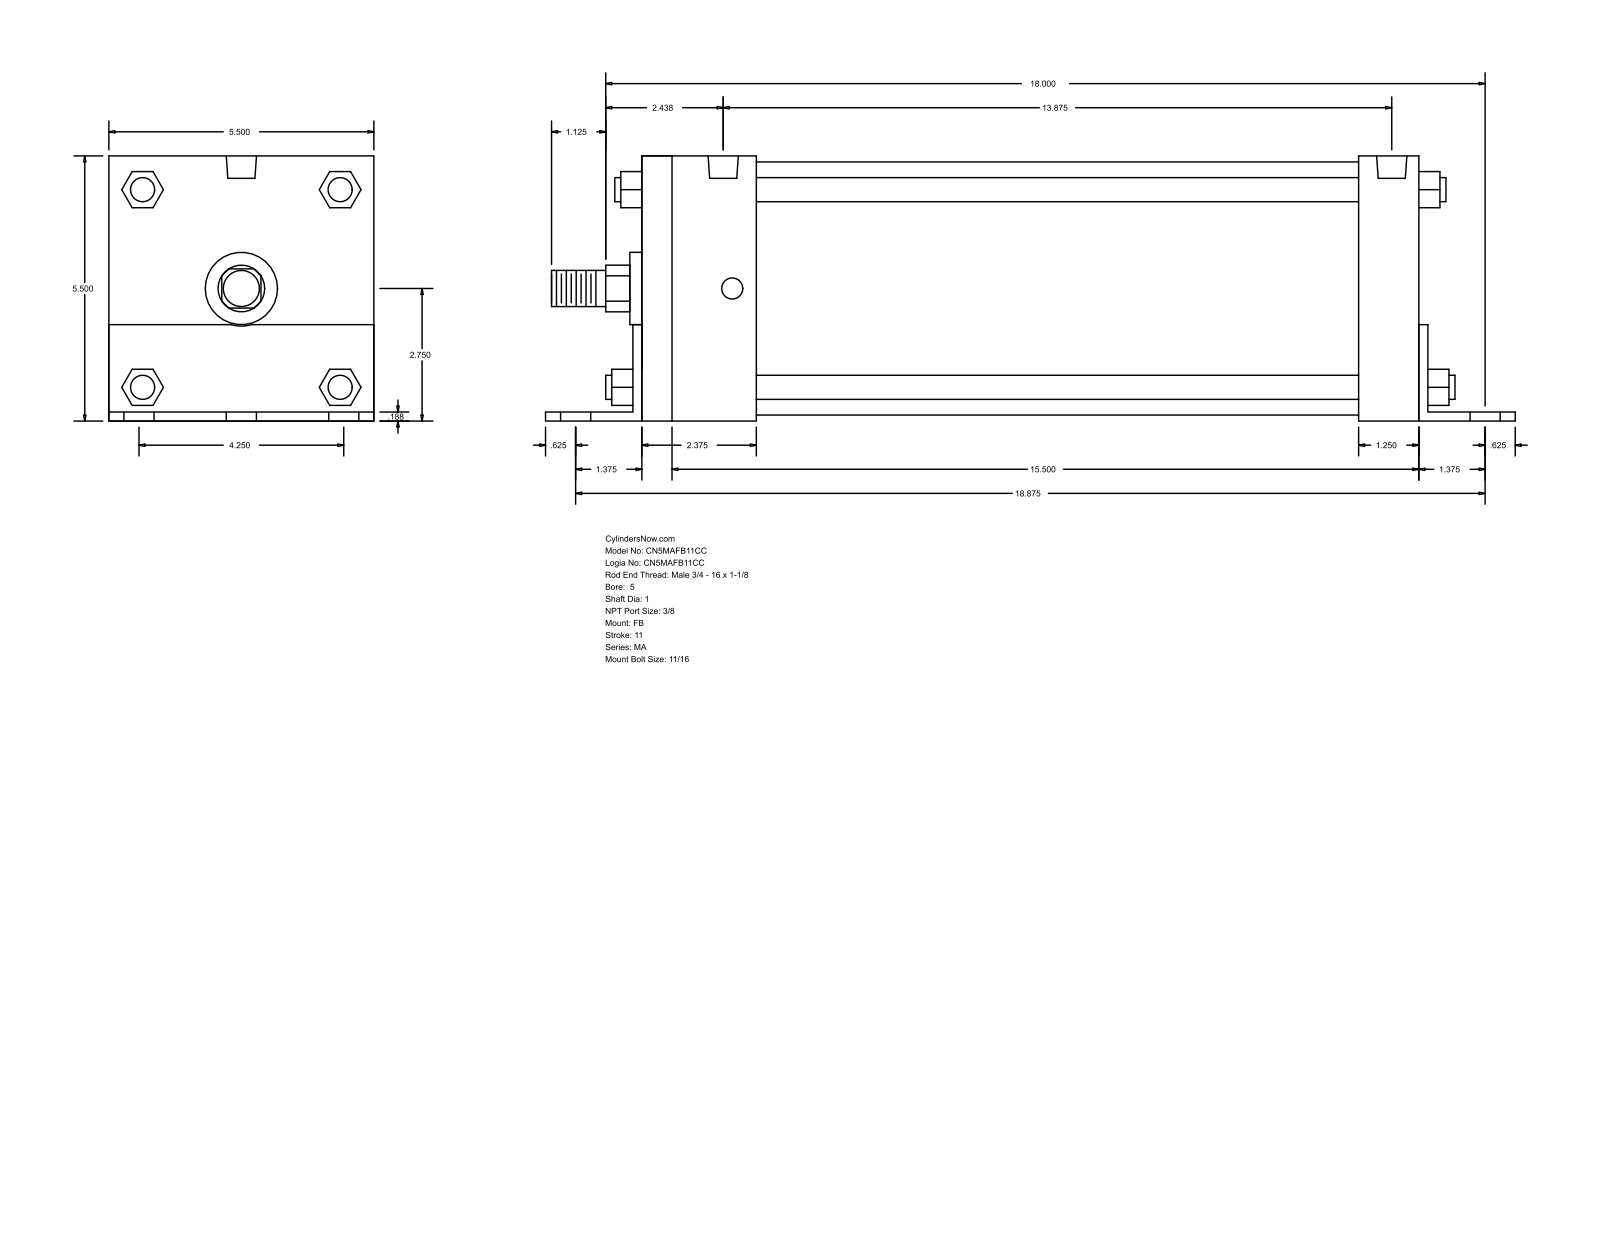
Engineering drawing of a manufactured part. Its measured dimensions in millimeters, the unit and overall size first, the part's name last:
Units: millimetres
Overall size (bounding box): 511.18 × 139.75 × 139.7
Round holes (diameter × count): ⌀17.46 ×6, ⌀11.11 ×4, ⌀15.93 ×2
Round bosses / shafts (diameter × count): ⌀12.7 ×4, ⌀133.35 ×1, ⌀38.1 ×1, ⌀25.4 ×1, ⌀19.05 ×1
Partial cylindrical surfaces — rounded edges, fillets, slot ends (radius × count): R12.29 ×1, R19.81 ×1
Main face-to-face distances: 139.7, 4.76, 139.75, 4.71, 134.99, 409.57, 4.77, 414.34, 414.33, 419.1
Hole centre spacings: 53.98, 482.46, 479.43, 73.04, 76.34, 94.68, 98.63, 107.96
Bodies: 0 solids, 140 faces (105 planar, 35 cylindrical, 0 other)
Part name (STEP PRODUCT): MA_FB__0500_1
STEP written by: GSSL Pune (CONFIG_CONTROL_DESIGN)
